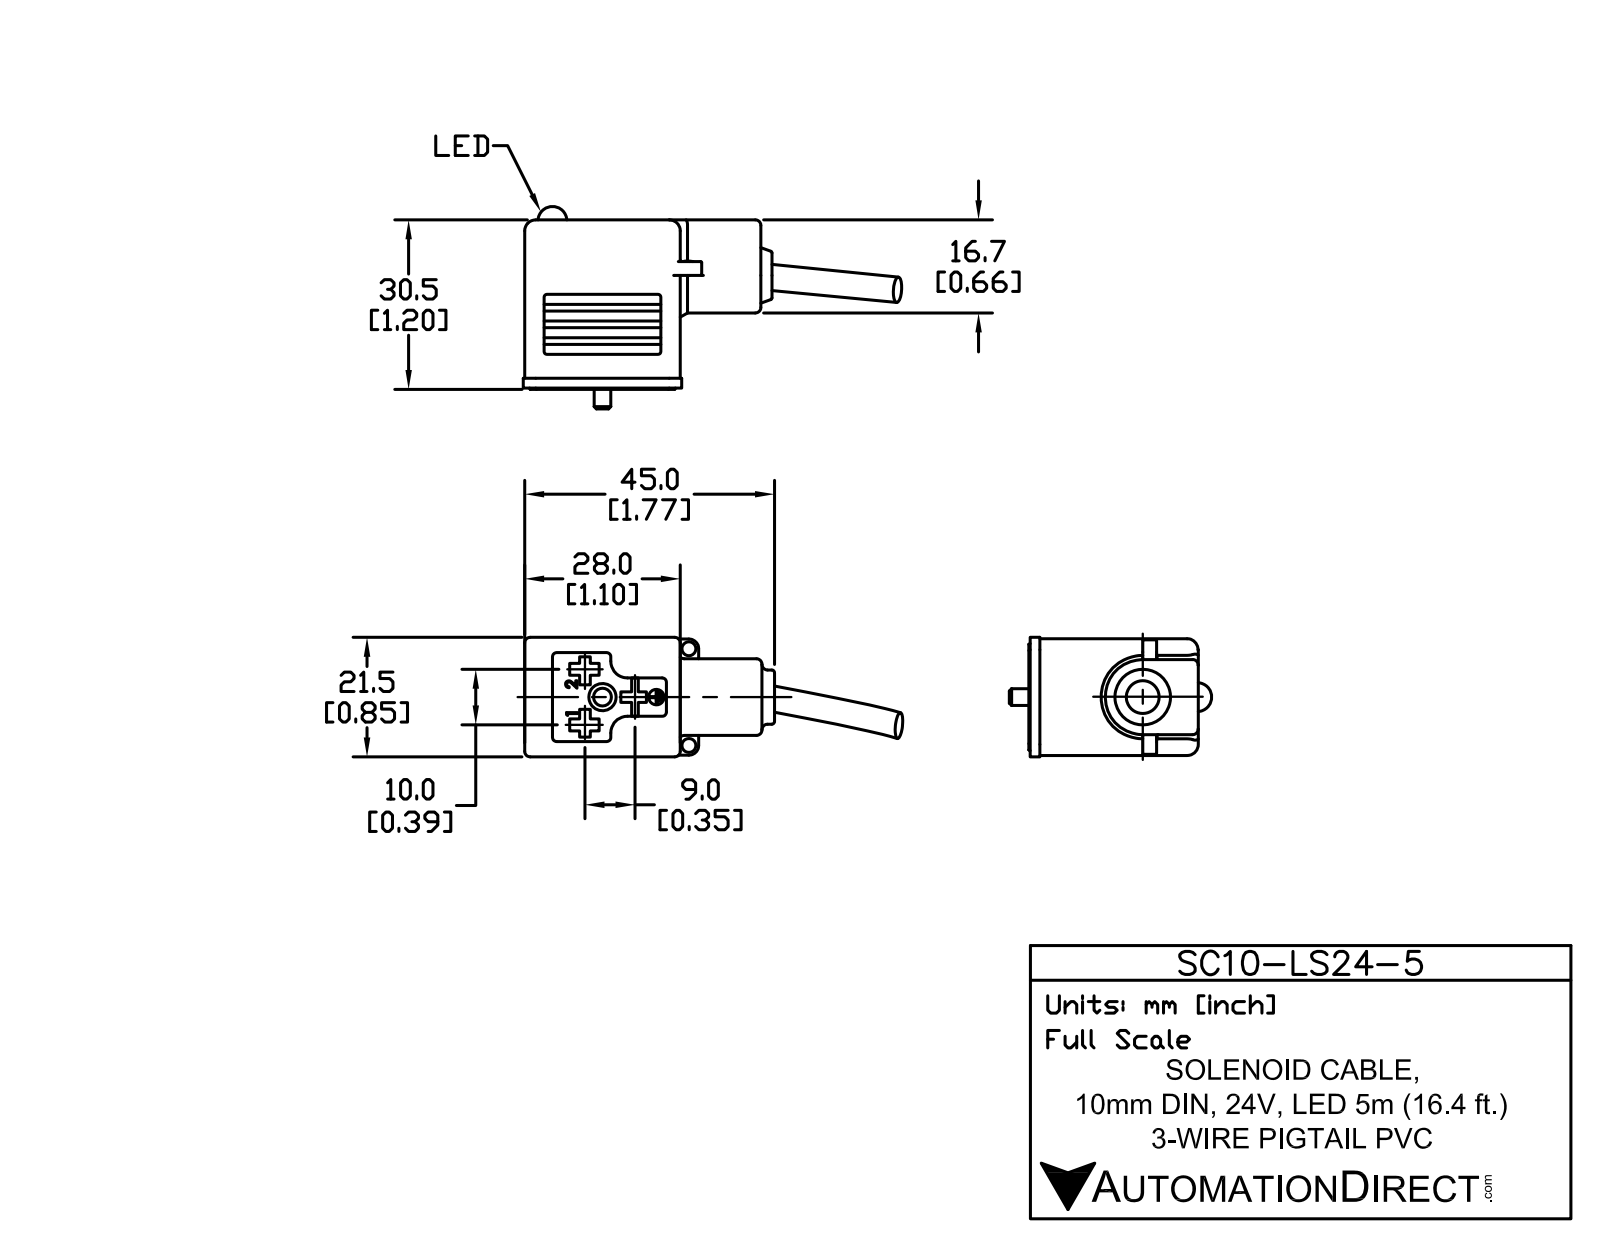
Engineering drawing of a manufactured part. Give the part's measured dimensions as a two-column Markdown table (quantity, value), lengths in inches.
| quantity | value |
| --- | --- |
| part name | SC10-LS24-5 |
| STEP written by | SolidWorks 2011 (AUTOMOTIVE_DESIGN) |
| units | inches |
| bodies | 2 solids, 204 faces (130 planar, 46 cylindrical, 28 other) |
| overall size | 2.668 × 1.449 × 0.846 |
| volume | 1.214 in³ |
| surface area | 10.55 in² |
| round holes (diameter × count) | 0.098 × 2, 0.109 × 1, 0.126 × 1, 0.193 × 1, 0.22 × 1, 0.26 × 1 |
| round bosses / shafts (diameter × count) | 0.384 × 1, 0.256 × 1, 0.118 × 1, 0.108 × 1 |
| partial cylindrical surfaces (radius × count) | 0.039 × 19, 0.03 × 6, 0.069 × 2, 0.118 × 2, 0.272 × 1 |
| main face-to-face distances | 0.823, 1.181, 1.079, 0.14, 1.102, 0.079, 0.683, 1.1, 1.179, 0.543 |
| hole center spacings | 0.413, 0.702, 0.382, 0.685 |
